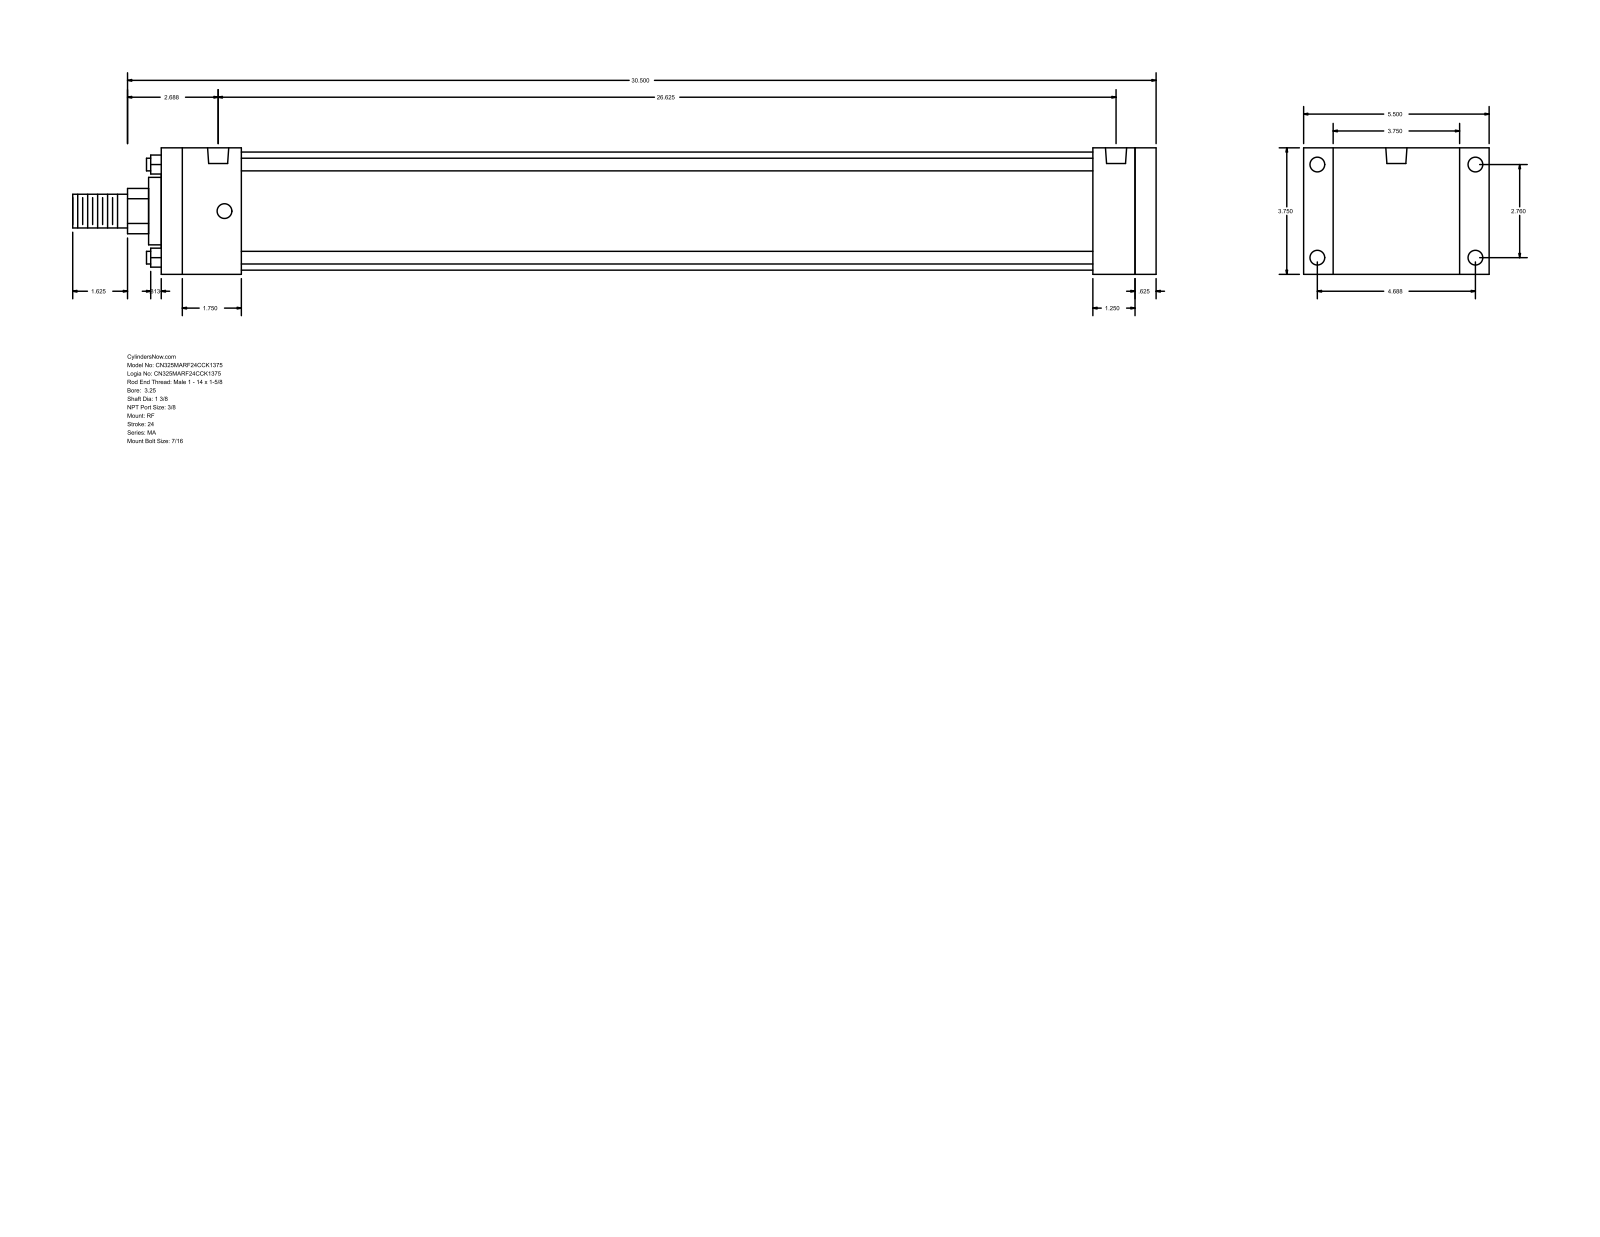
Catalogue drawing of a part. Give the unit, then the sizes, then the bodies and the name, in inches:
Units: inches
Overall size (bounding box): 32.125 × 5.5 × 3.75
Round holes (diameter × count): ⌀0.437 ×8, ⌀0.627 ×2
Round bosses / shafts (diameter × count): ⌀0.375 ×4, ⌀3.5 ×1, ⌀2 ×1, ⌀1.375 ×1, ⌀1 ×1
Partial cylindrical surfaces — rounded edges, fillets, slot ends (radius × count): R0.672 ×1
Main face-to-face distances: 3.75, 29.5, 28.875, 0.625, 0.875, 4.625, 27.625, 1.25, 1.875, 2.375
Hole centre spacings: 0.188, 2.76, 4.687, 5.439, 26.25, 26.437, 26.625
Bodies: 0 solids, 92 faces (64 planar, 28 cylindrical, 0 other)
Part name (STEP PRODUCT): MA_RF__0325_1.375
STEP written by: GSSL Pune (CONFIG_CONTROL_DESIGN)
